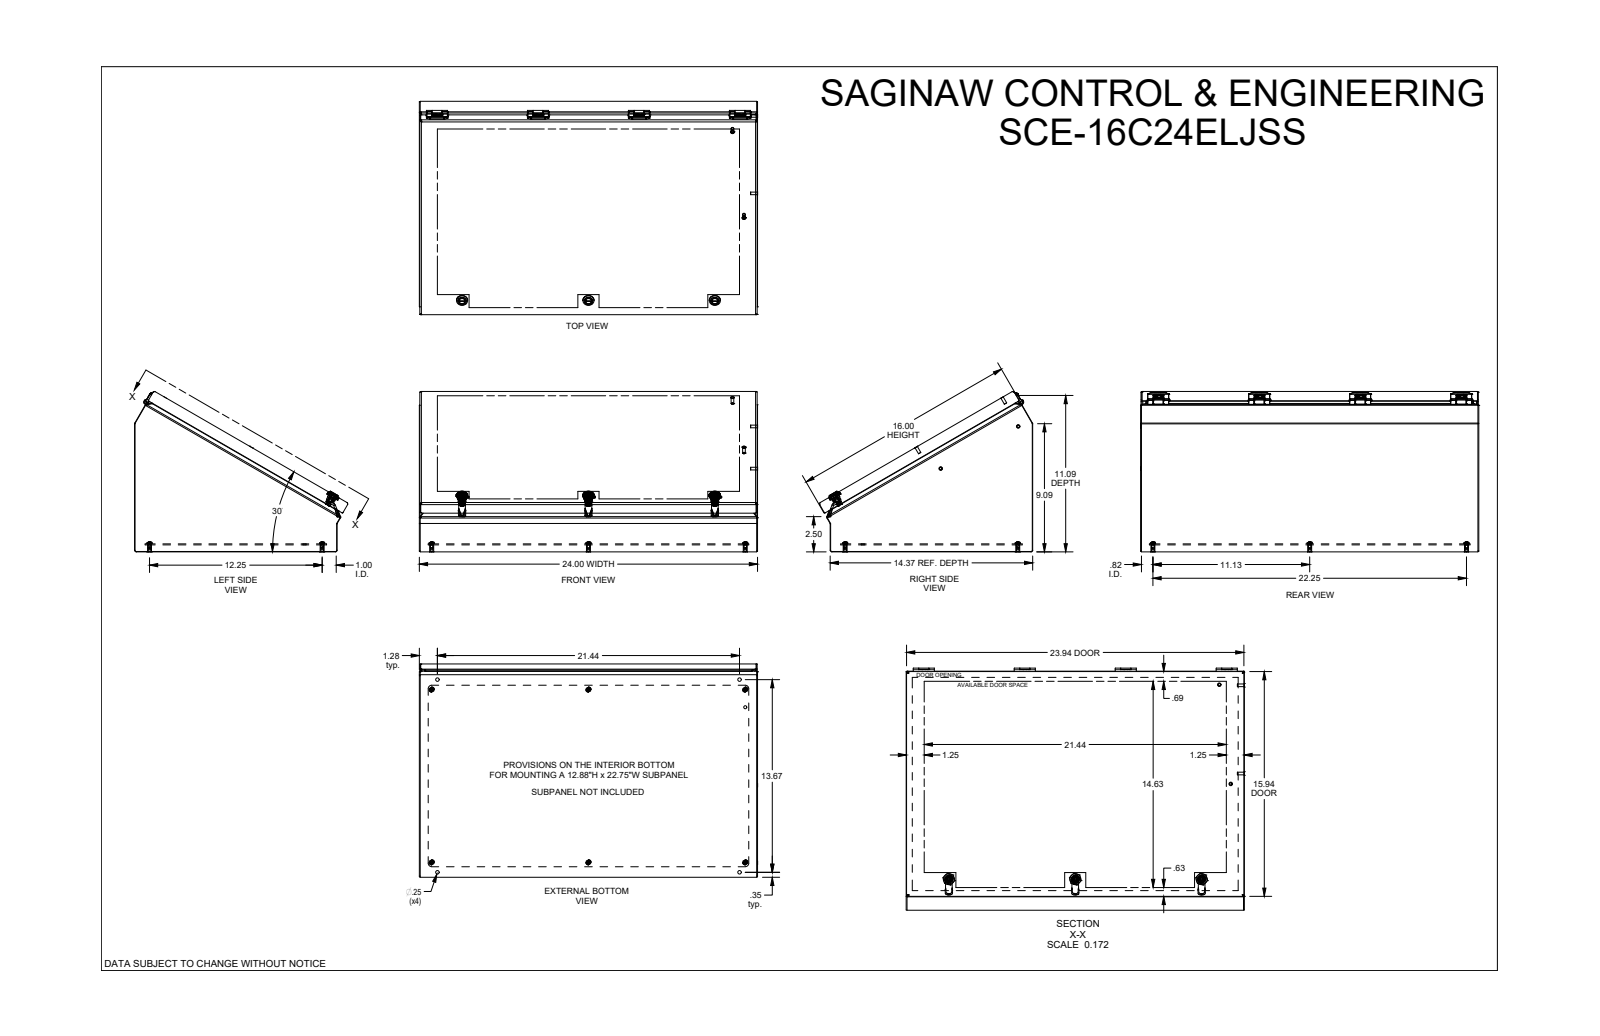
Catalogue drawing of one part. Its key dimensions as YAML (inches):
part_name: "SCE-16C24ELJ"
step_written_by: "SolidWorks 2019 (AUTOMOTIVE_DESIGN)"
units: inches
bodies: {solids: 46, faces: 1740, planar: 668, cylindrical: 706, other: 366}
overall_size: [24.004, 15.13, 11.38]
volume: 111.1
surface_area: 3478
round_holes:
  - {diameter: 0.25, count: 10}
  - {diameter: 0.19, count: 6}
  - {diameter: 0.281, count: 6}
  - {diameter: 0.02, count: 4}
  - {diameter: 0.1, count: 4}
  - {diameter: 0.174, count: 4}
  - {diameter: 0.193, count: 4}
  - {diameter: 0.266, count: 4}
  - {diameter: 0.2, count: 3}
  - {diameter: 0.239, count: 3}
  - {diameter: 0.254, count: 3}
  - {diameter: 0.269, count: 3}
round_bosses_or_shafts:
  - {diameter: 0.28, count: 6}
  - {diameter: 0.26, count: 4}
  - {diameter: 0.256, count: 4}
  - {diameter: 0.188, count: 4}
  - {diameter: 0.18, count: 4}
  - {diameter: 0.788, count: 3}
  - {diameter: 0.548, count: 3}
  - {diameter: 0.46, count: 3}
partial_cylinders:
  - {radius: 0.03, count: 48}
  - {radius: 0.013, count: 41}
  - {radius: 0.01, count: 30}
  - {radius: 0.06, count: 26}
  - {radius: 0.015, count: 24}
  - {radius: 0.02, count: 17}
  - {radius: 0.12, count: 16}
  - {radius: 0.063, count: 10}
face_to_face_distances: [0.06, 0.075, 0.436, 0.496, 0.511, 0.571, 23.94, 0.06, 23.88, 24]
hole_center_spacings: [0.818, 7.167, 10.743, 11.125, 12.966, 14.333, 16.548, 16.818]
